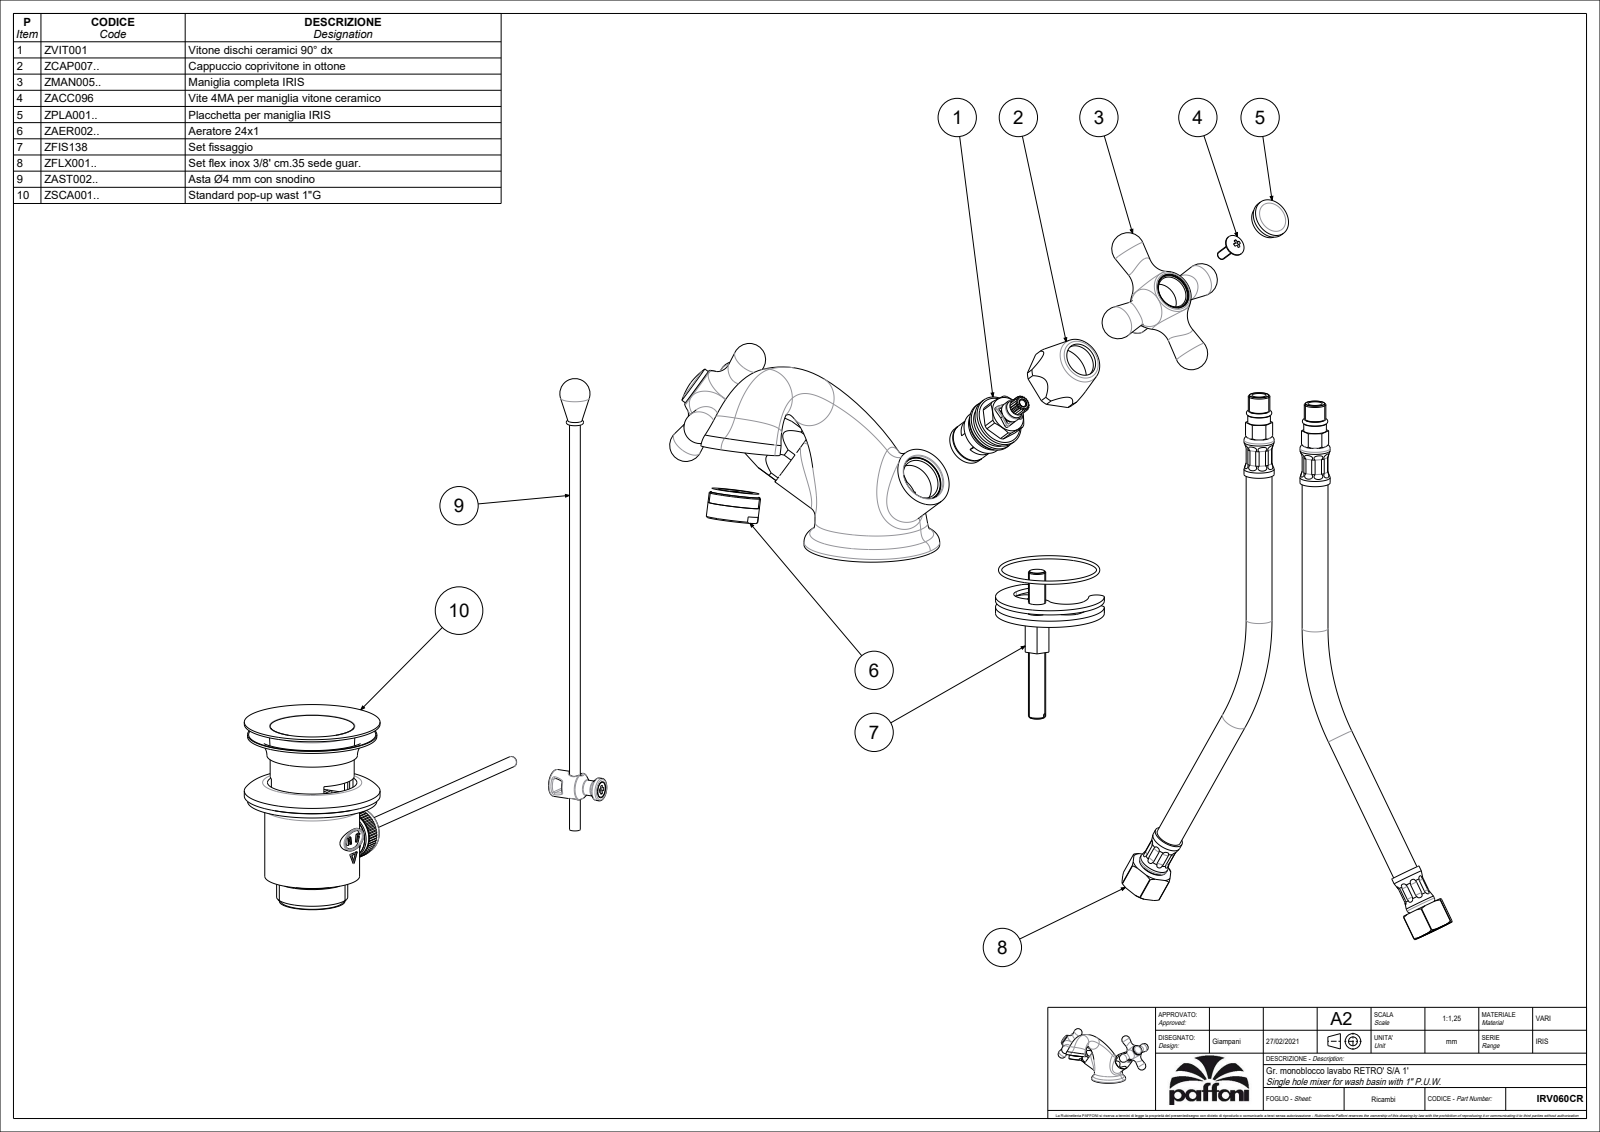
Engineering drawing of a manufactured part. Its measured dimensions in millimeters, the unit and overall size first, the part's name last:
Units: millimetres
Overall size (bounding box): 185.61 × 171.45 × 106.41
Round holes (diameter × count): ⌀9 ×4, ⌀21 ×3, ⌀11 ×2, ⌀19 ×2, ⌀21.5 ×2, ⌀5.5 ×1, ⌀6.8 ×1, ⌀16.5 ×1, ⌀20 ×1, ⌀23 ×1, ⌀49 ×1
Round bosses / shafts (diameter × count): ⌀28 ×2, ⌀18 ×2, ⌀13.5 ×2, ⌀63 ×1, ⌀44 ×1, ⌀24 ×1
Partial cylindrical surfaces — rounded edges, fillets, slot ends (radius × count): R14.5 ×2, R5 ×1
Main face-to-face distances: 21.91, 7.7, 1.3, 8.5, 7.8, 26.51, 19.01, 6, 24.1, 46.01
Hole centre spacings: 7.5, 12.66, 13.48, 10.2, 11.2, 15, 21.4
Volume: 180 371 mm³ · Surface area: 64 901 mm²
Bodies: 1 solid, 325 faces (82 planar, 73 cylindrical, 170 other)
Part name (STEP PRODUCT): IRV060CR
STEP written by: CREO PARAMETRIC BY PTC INC, 2020044 (CONFIG_CONTROL_DESIGN)
